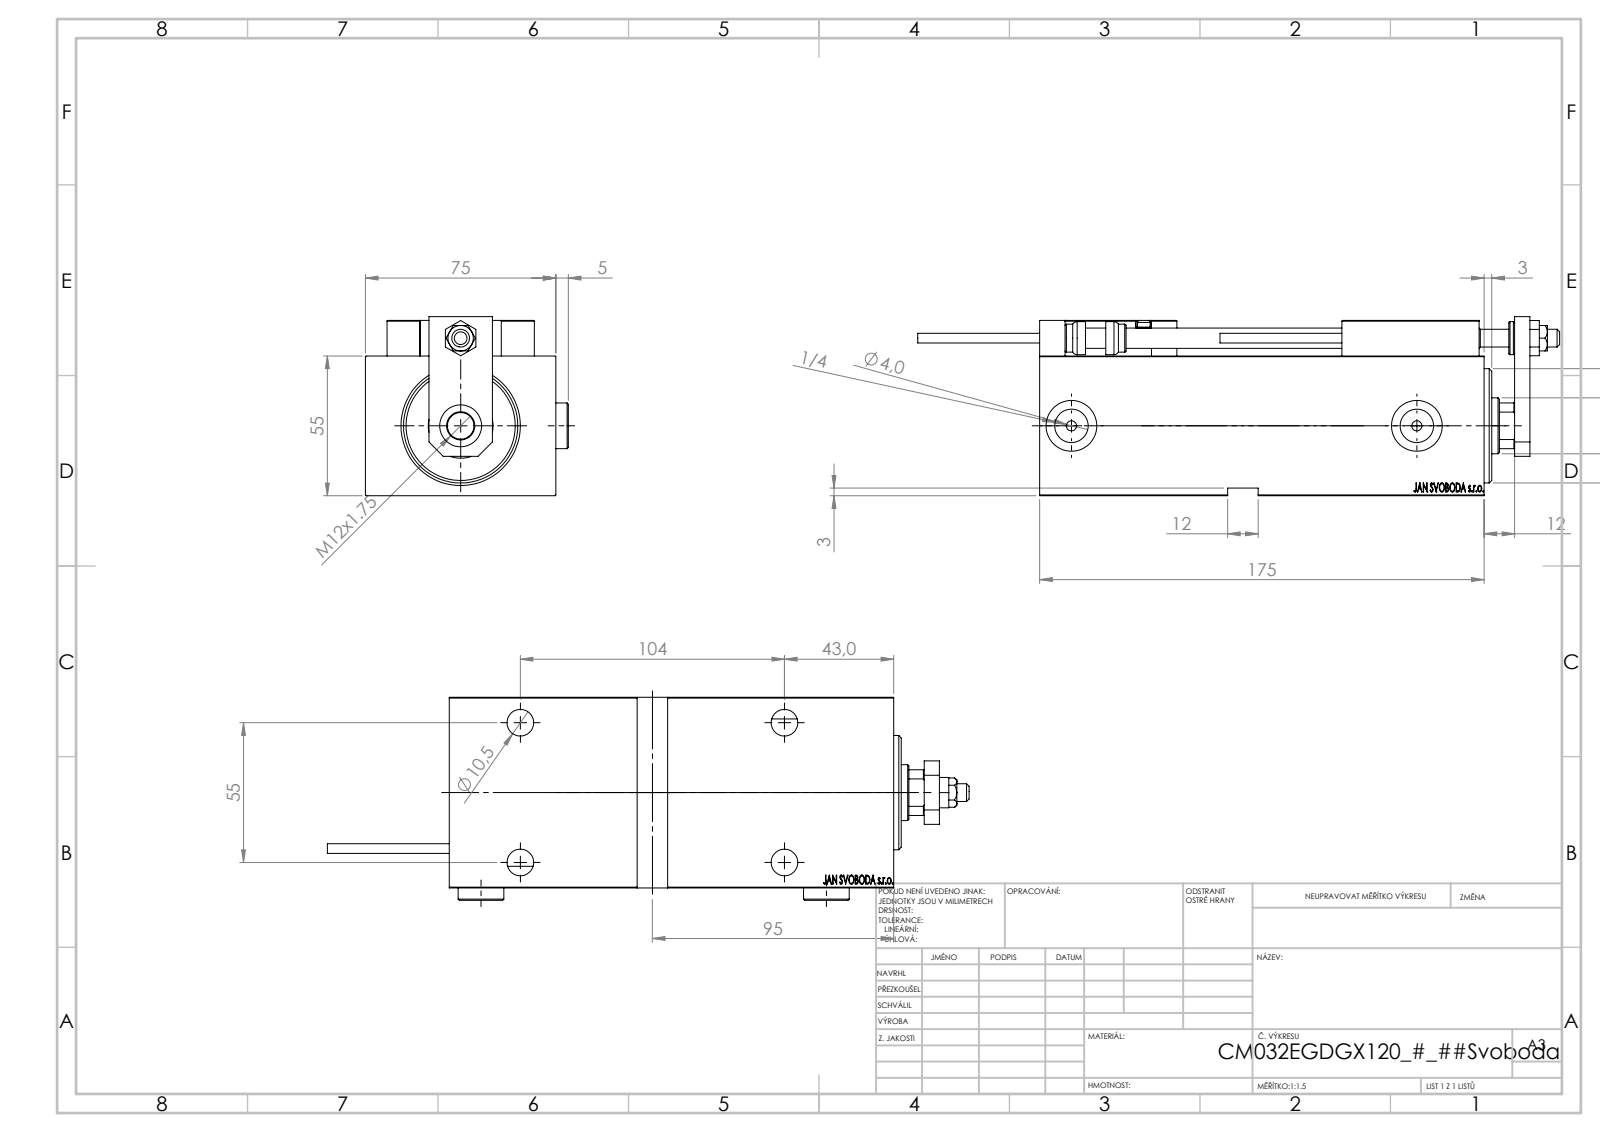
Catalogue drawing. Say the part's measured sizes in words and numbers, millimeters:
The part is named "SWITCH X; KONCOVKA; SWITCH DIM B,W; ALLEN BOLT D8 (+7 more)". Its 3-D file was written by "SolidWorks 2019 (CONFIG_CONTROL_DESIGN)". It is 26 solids with 1346 faces: 605 planar, 196 cylindrical and 545 other. Overall it measures 252.7 by 79.9 by 70.5 millimeters. Its volume is 697 426 cubic millimeters and its surface area 131 217 square millimeters. Round holes: 6 of diameter 4, 5 of diameter 8, 5 of diameter 10.5, 5 of diameter 16.5, 4 of diameter 3.2, 2 of diameter 5, 2 of diameter 13.16, 2 of diameter 20, 1 of diameter 7, 1 of diameter 22, 1 of diameter 25.5, 1 of diameter 32. Round bosses or shafts: 2 of diameter 18, 2 of diameter 5, 2 of diameter 3.8, 1 of diameter 34, 1 of diameter 13, 1 of diameter 11. Partial cylindrical surfaces (rounded edges, fillets, slot ends): 30 of radius 0.3, 2 of radius 3, 1 of radius 10.5. The main face-to-face distances are 55, 75, 10, 3, 14, 12, 175, 5, 69, 165. The hole center spacings are 11.37, 20, 28.9, 29.59, 29.69, 36.06, 40.03, 42.19.
